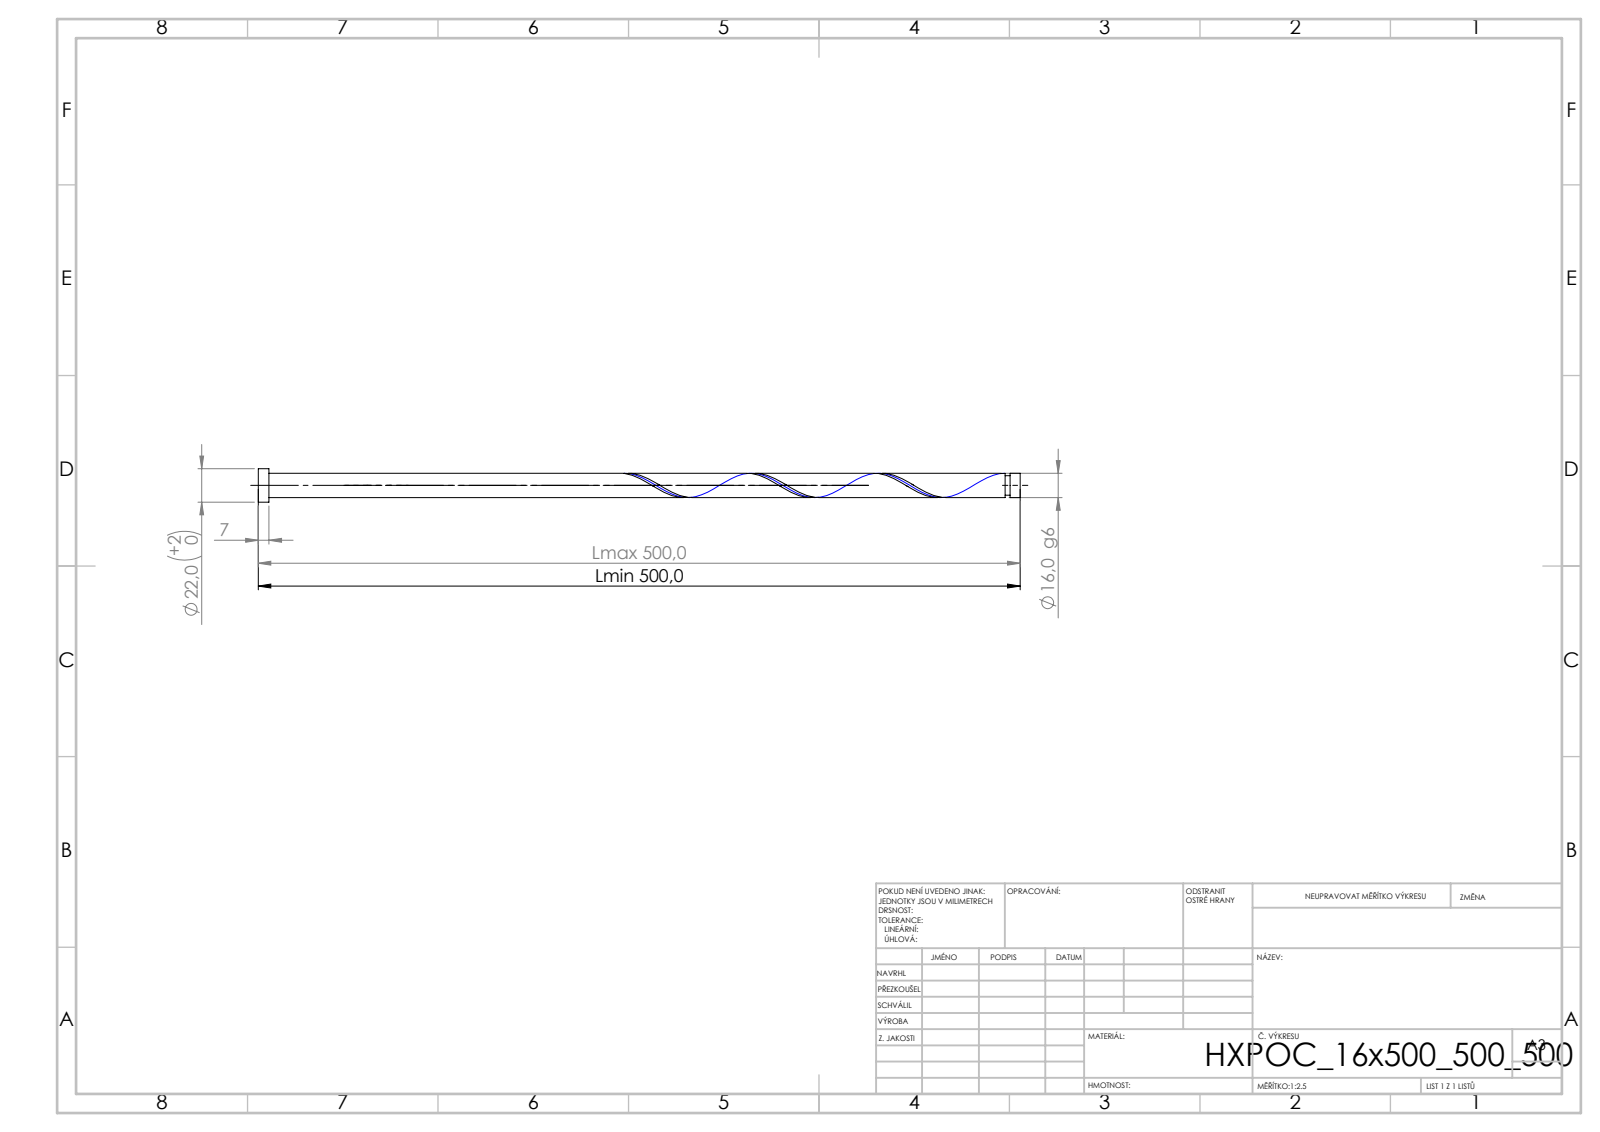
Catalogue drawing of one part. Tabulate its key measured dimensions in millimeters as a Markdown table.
| quantity | value |
| --- | --- |
| STEP written by | SolidWorks 2019 (CONFIG_CONTROL_DESIGN) |
| units | millimeters |
| bodies | 1 solid, 21 faces (6 planar, 14 cylindrical, 1 other) |
| overall size | 500 × 22 × 22 |
| volume | 100 590 mm³ |
| surface area | 26 607 mm² |
| round bosses / shafts (diameter × count) | 22 × 1, 16 × 1, 12.8 × 1 |
| main face-to-face distances | 500, 7, 493, 493.35, 486.35, 6.65, 490.15, 483.15, 3.2, 9.85 |
